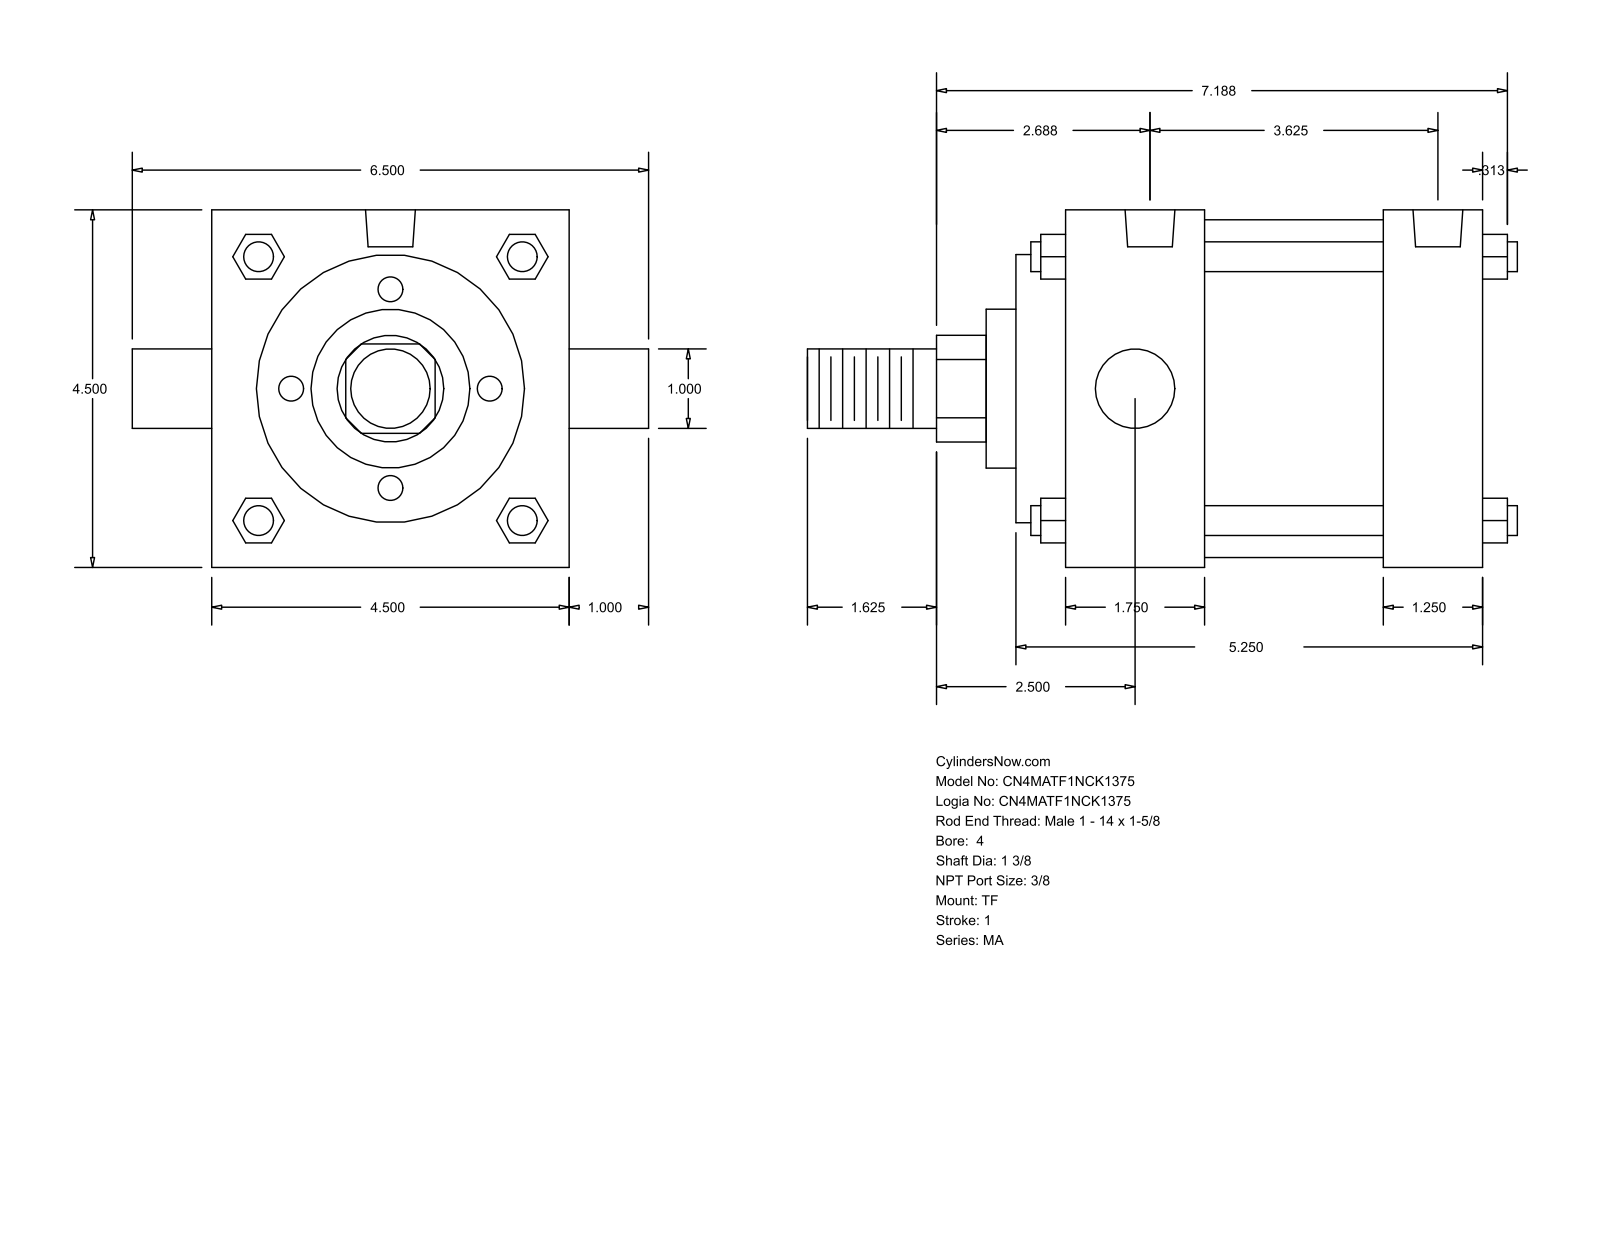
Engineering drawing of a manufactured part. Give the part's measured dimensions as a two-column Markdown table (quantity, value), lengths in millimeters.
| quantity | value |
| --- | --- |
| part name | MA_TF__0400_1.375 |
| STEP written by | GSSL Pune (CONFIG_CONTROL_DESIGN) |
| units | millimeters |
| bodies | 0 solids, 122 faces (93 planar, 29 cylindrical, 0 other) |
| overall size | 227.01 × 165.1 × 114.3 |
| round holes (diameter × count) | 11.11 × 3, 15.93 × 2 |
| round bosses / shafts (diameter × count) | 9.53 × 4, 25.4 × 2, 107.95 × 1, 85.72 × 1, 50.8 × 1, 34.92 × 1 |
| partial cylindrical surfaces (radius × count) | 17.06 × 1 |
| main face-to-face distances | 114.3, 133.35, 149.22, 15.87, 117.48, 101.61, 31.74, 60.32, 44.45, 57.16 |
| hole center spacings | 4.77, 87.31, 82.54, 92.08 |
